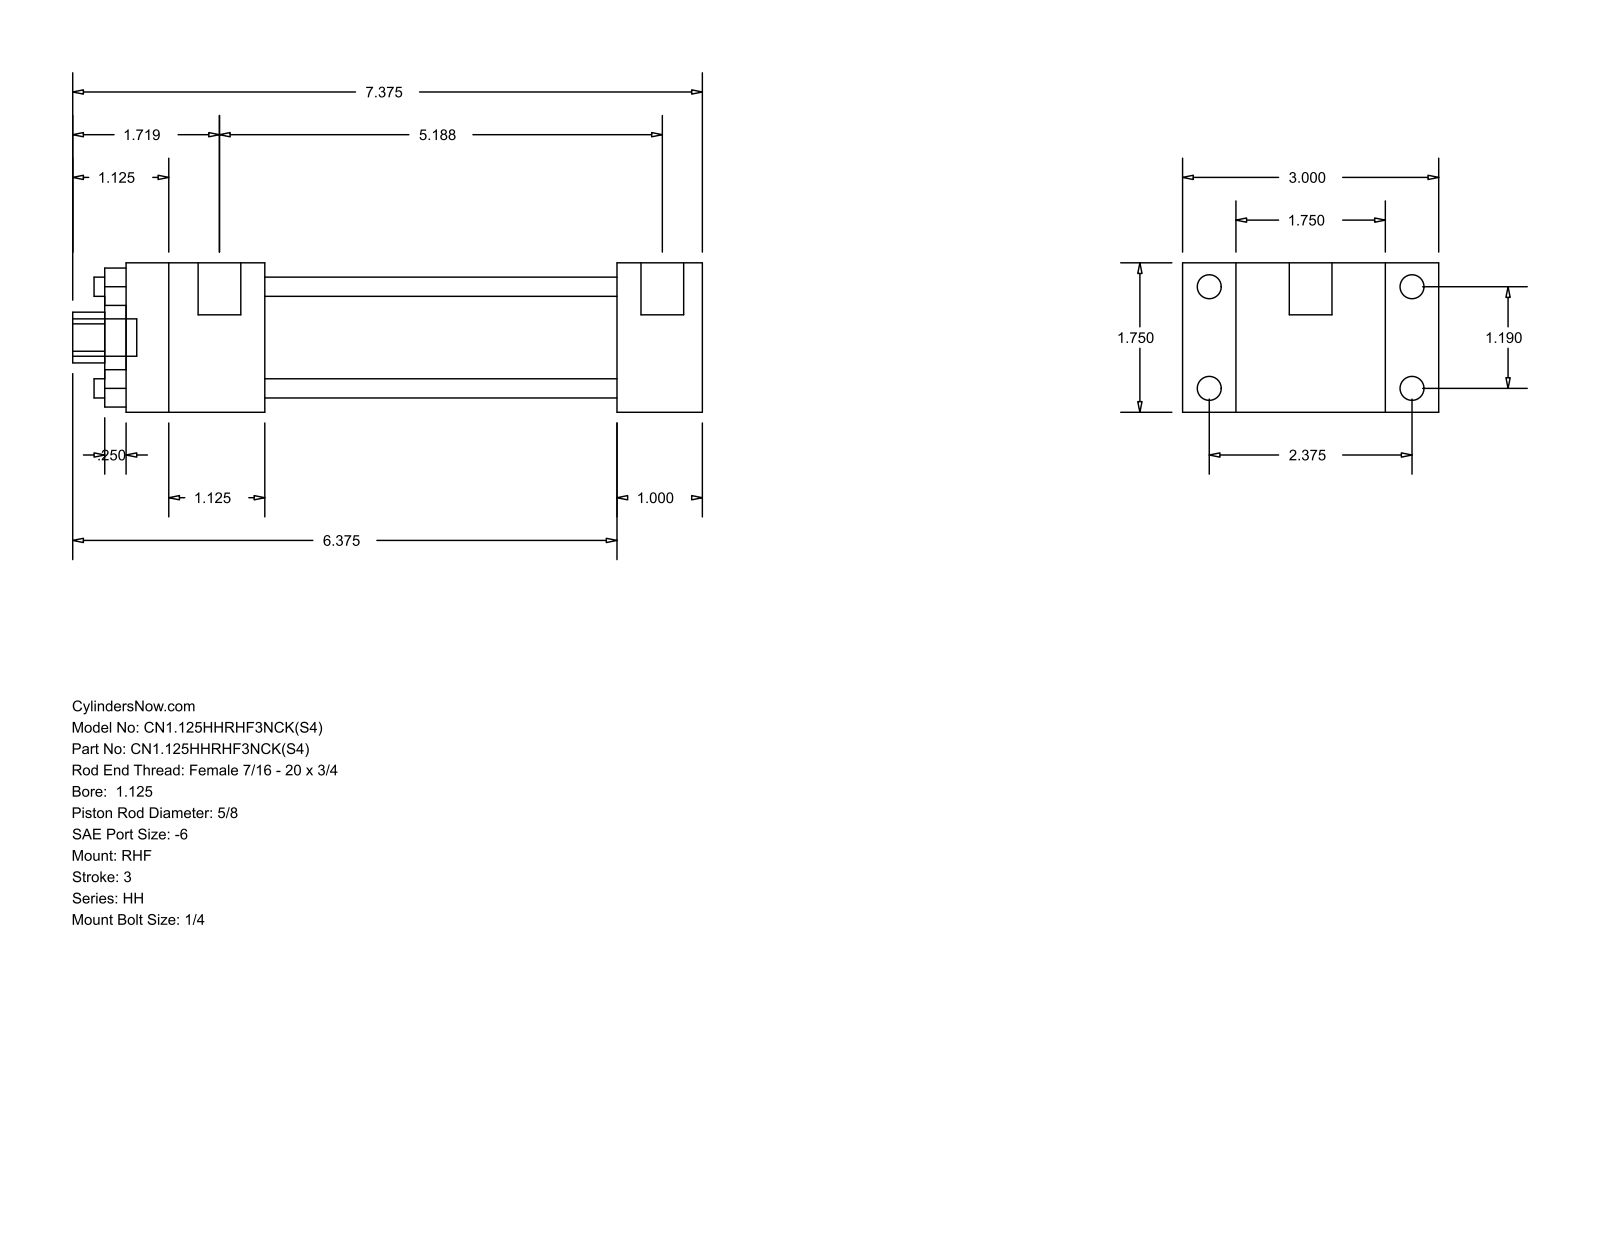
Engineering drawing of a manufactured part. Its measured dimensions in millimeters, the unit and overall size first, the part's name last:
Units: millimetres
Overall size (bounding box): 187.32 × 76.2 × 44.45
Round holes (diameter × count): ⌀5.71 ×4, ⌀15.88 ×1, ⌀28.57 ×1, ⌀34.92 ×1
Round bosses / shafts (diameter × count): ⌀7.14 ×4, ⌀5.56 ×4, ⌀12.7 ×2, ⌀11.11 ×1
Partial cylindrical surfaces — rounded edges, fillets, slot ends (radius × count): R7.54 ×1
Main face-to-face distances: 44.46, 15.87, 60.33, 25.39, 76.2, 104.78, 130.17, 41.27, 146.05, 171.44
Hole centre spacings: 21.37, 30.22, 42.74
Bodies: 0 solids, 88 faces (60 planar, 28 cylindrical, 0 other)
Part name (STEP PRODUCT): HH_RHF__0112_0.625
STEP written by: GSSL Pune (CONFIG_CONTROL_DESIGN)
